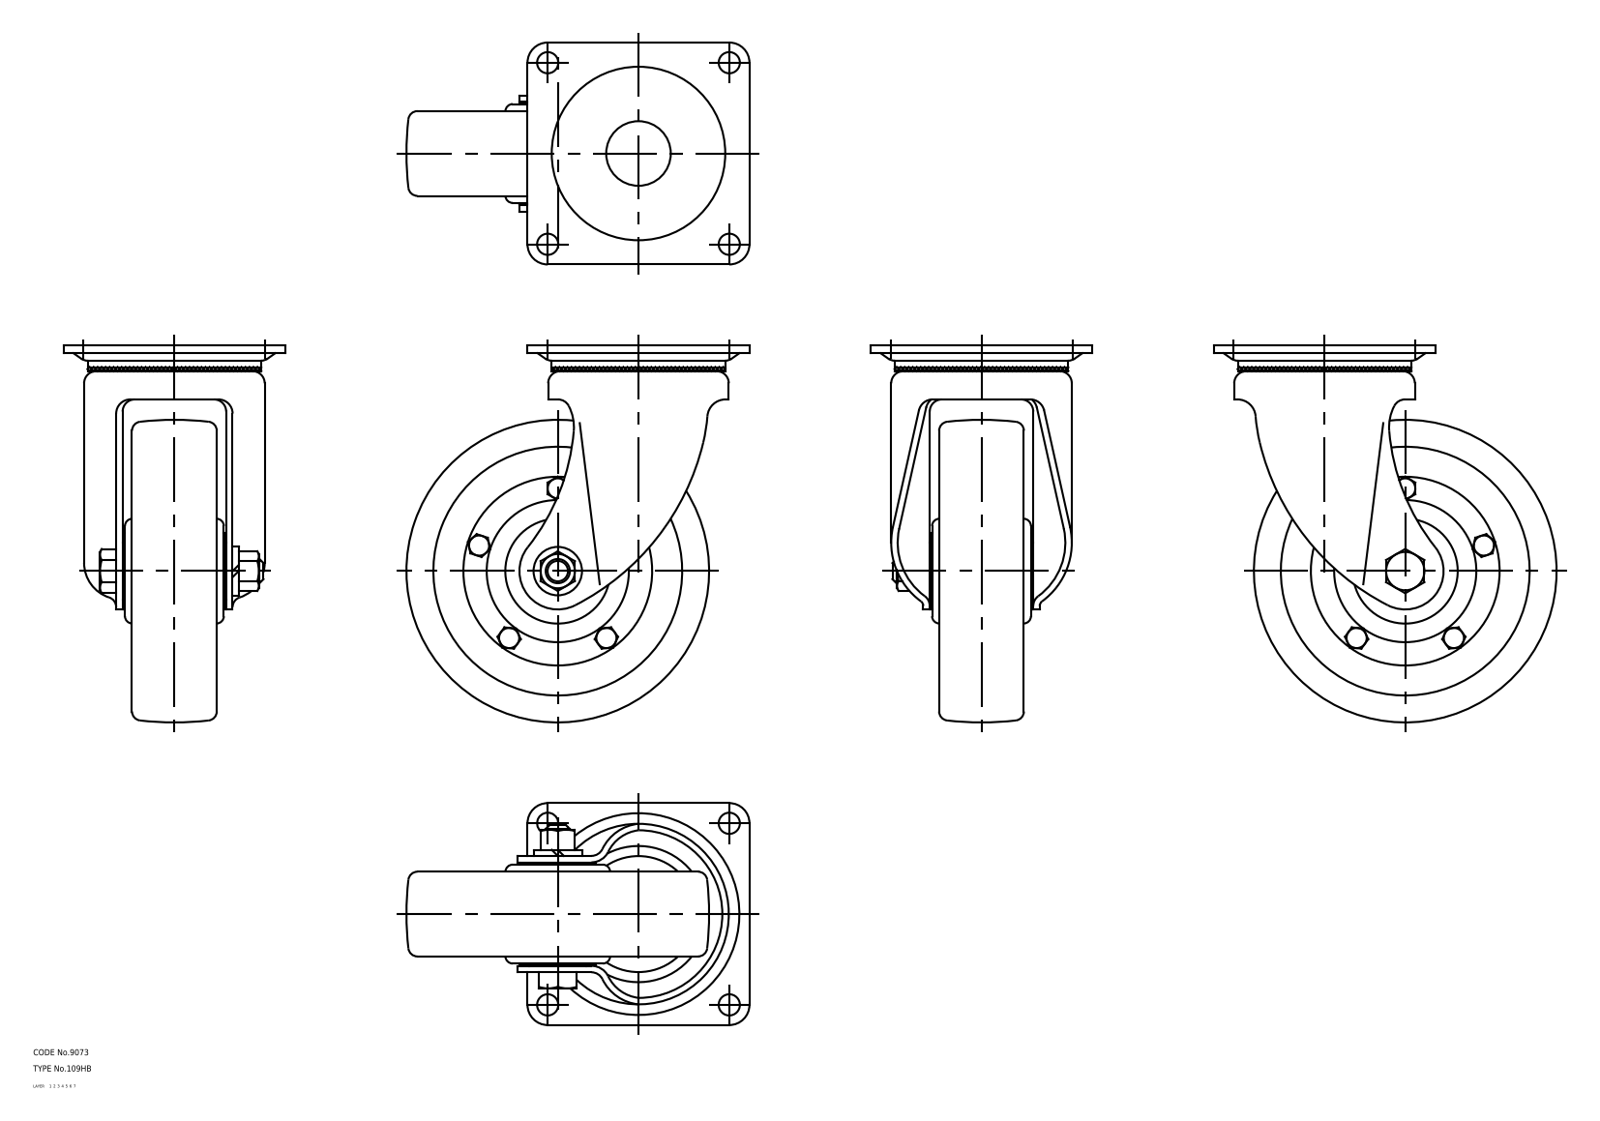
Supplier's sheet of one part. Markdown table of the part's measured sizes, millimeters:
| quantity | value |
| --- | --- |
| part name | 67130831; 67130844; 67130857; 67130870 (+1 more) |
| STEP written by | CADfix (AUTOMOTIVE_DESIGN) |
| units | millimeters |
| bodies | 5 solids, 381 faces (0 planar, 0 cylindrical, 381 other) |
| overall size | 187 × 170 × 110 |
| volume | 863 696 mm³ |
| surface area | 146 279 mm² |
